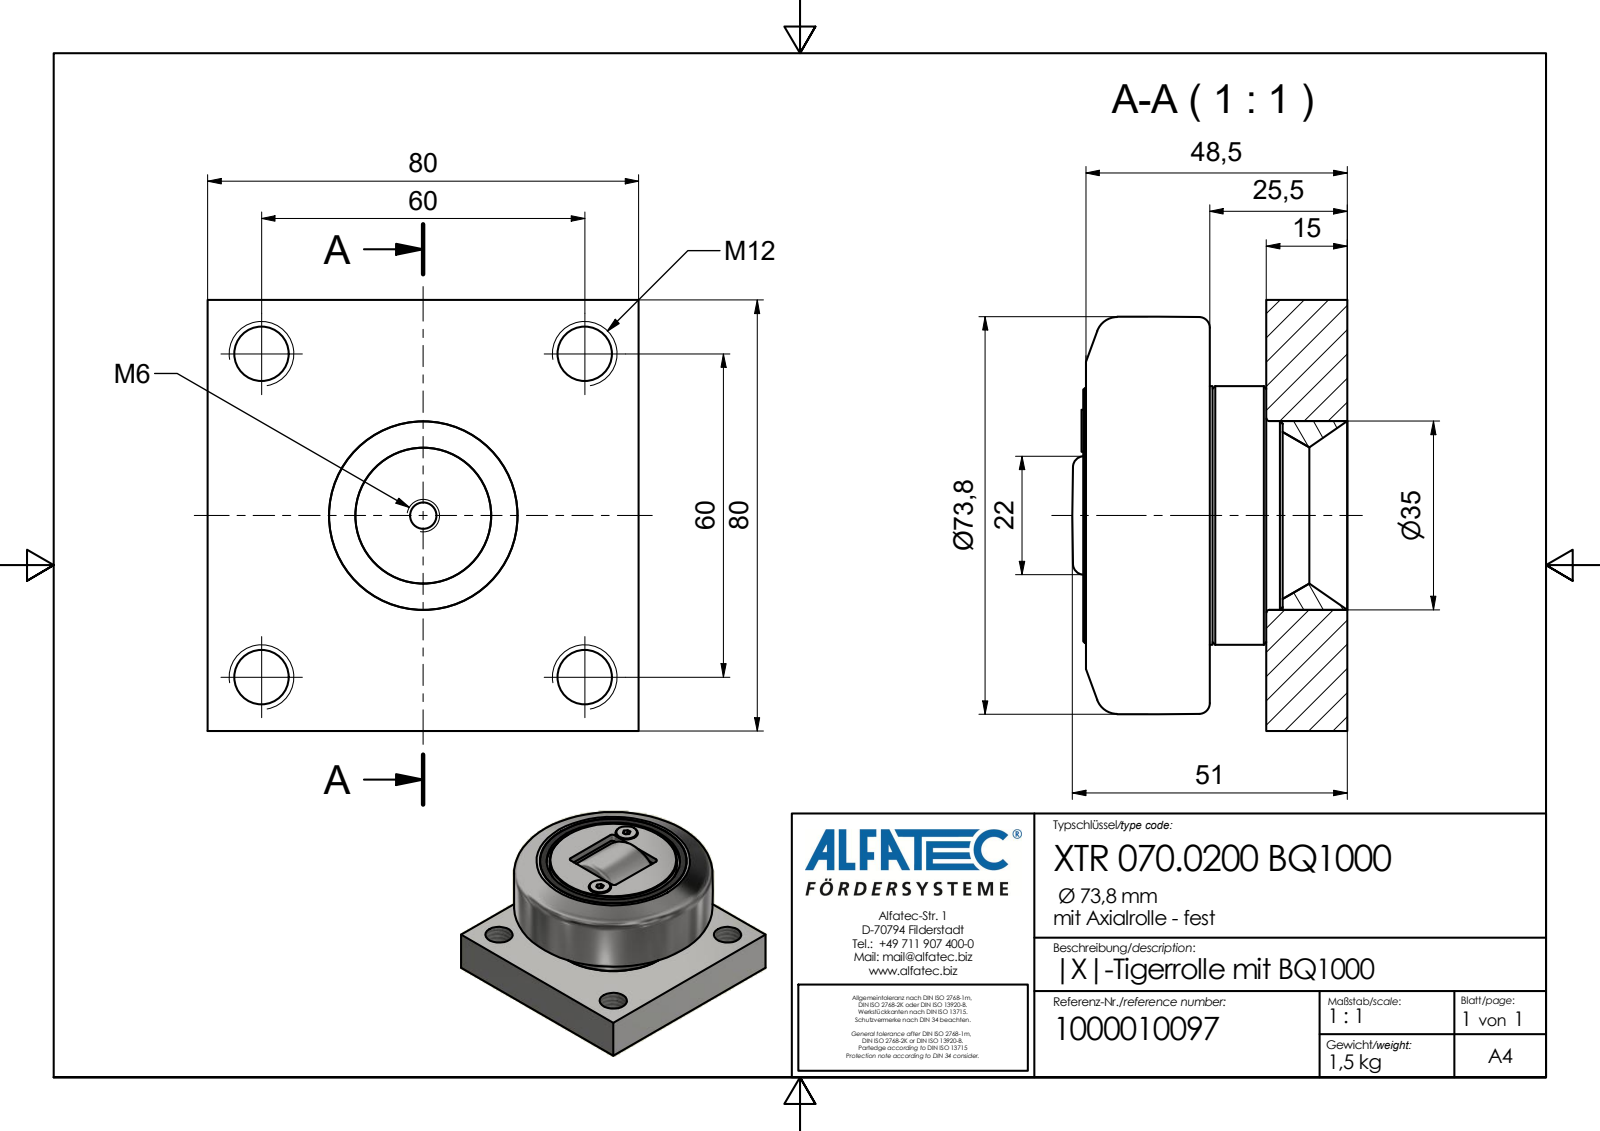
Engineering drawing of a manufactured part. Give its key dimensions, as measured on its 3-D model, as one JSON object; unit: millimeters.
{"part_name": "XTR 070.0200 BQ1000_Kontur", "step_written_by": "Autodesk Inventor 2020 (AP242_MANAGED_MODEL_BASED_3D_ENGINEERING_MIM_LF)", "units": "millimeters", "bodies": {"solids": 1, "faces": 64, "planar": 36, "cylindrical": 15, "other": 13}, "overall_size": [80, 80, 51], "volume_mm3": 201014, "surface_area_mm2": 30758, "round_holes": [[10.11, 4], [2.5, 1], [4.92, 1]], "round_bosses_or_shafts": [[7.8, 2], [48, 1], [47.3, 1]], "partial_cylinders_radius": [[1, 4]], "face_to_face_distances": [15, 80, 25.5, 10.5, 23.5, 0.5, 49, 34, 23, 48.5], "hole_center_spacings": [42.43, 60, 84.85]}
